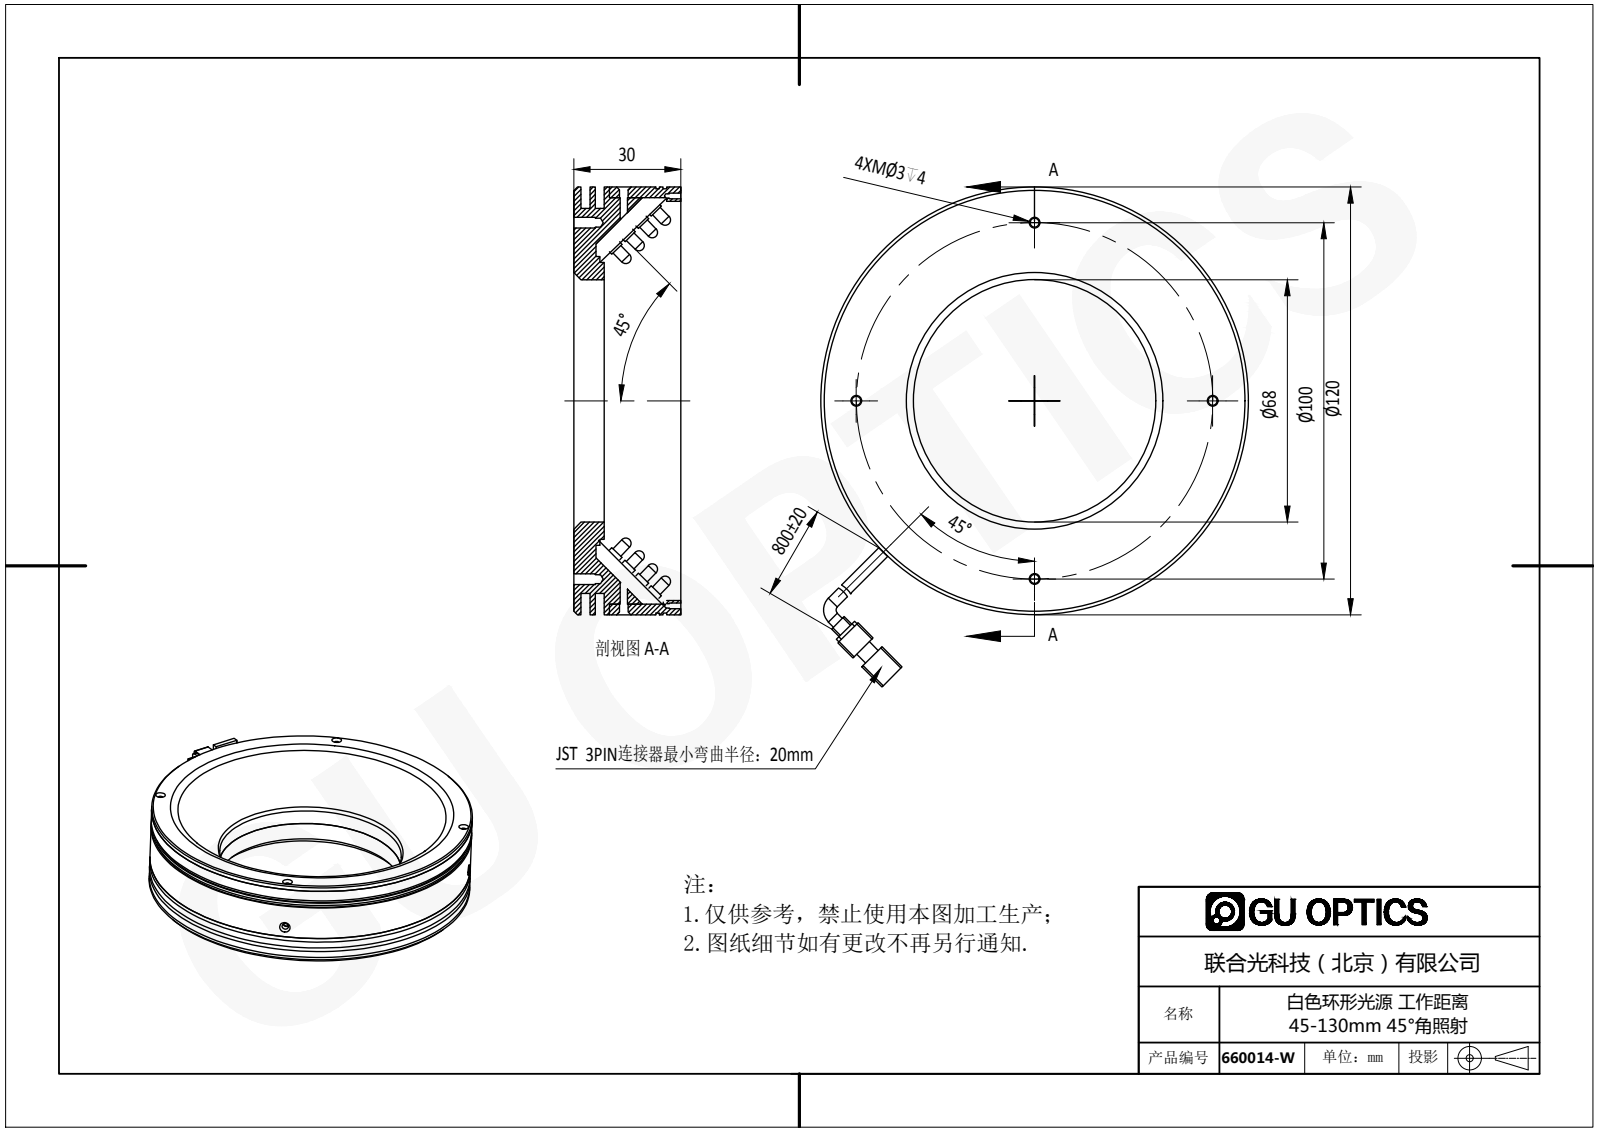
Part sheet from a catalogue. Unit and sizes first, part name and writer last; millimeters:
Units: millimetres
Overall size (bounding box): 140.26 × 120 × 32
Round holes (diameter × count): ⌀1.2 ×4, ⌀1.6 ×4, ⌀1.7 ×4, ⌀2.5 ×4, ⌀3 ×4, ⌀3.5 ×4, ⌀2 ×2, ⌀2.4 ×2, ⌀68 ×1, ⌀112 ×1
Round bosses / shafts (diameter × count): ⌀3.8 ×260, ⌀3 ×260, ⌀3.5 ×2, ⌀120 ×1, ⌀119 ×1, ⌀114 ×1, ⌀108 ×1, ⌀81 ×1
Partial cylindrical surfaces — rounded edges, fillets, slot ends (radius × count): R0.5 ×8, R1 ×4, R1.6 ×1, R6 ×1
Main face-to-face distances: 4, 30, 2, 2.5, 1.5, 21.5, 8.5, 6, 24, 20
Hole centre spacings: 76.2, 7.5, 50, 57.5, 70.71, 81.32, 107.5, 100
Volume: 128 993 mm³ · Surface area: 114 112 mm²
Bodies: 266 solids, 4721 faces (3214 planar, 1182 cylindrical, 325 other)
Part name (STEP PRODUCT): 660014-W
STEP written by: SolidWorks 2016 (AUTOMOTIVE_DESIGN)
